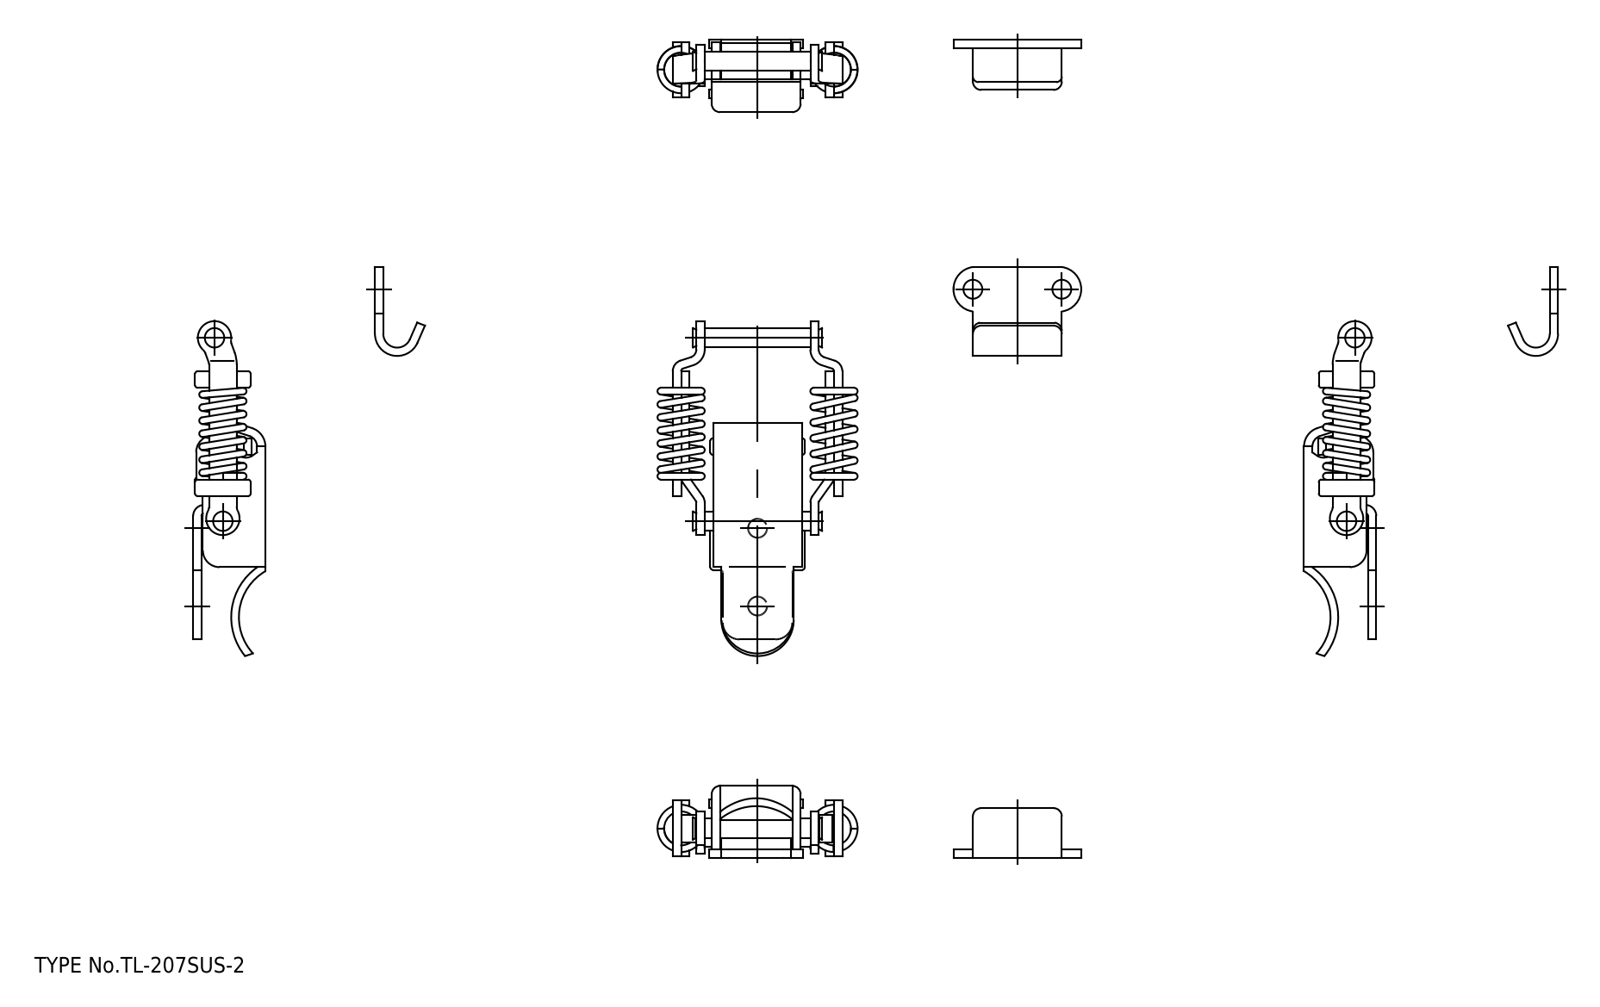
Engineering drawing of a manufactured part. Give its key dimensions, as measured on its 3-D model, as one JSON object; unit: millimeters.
{"part_name": "armA; base; spring; armB (+2 more)", "step_written_by": "spGate 19.8.4 (****-****-****-****) (AUTOMOTIVE_DESIGN)", "units": "millimeters", "bodies": {"solids": 7, "faces": 254, "planar": 124, "cylindrical": 98, "other": 32}, "overall_size": [69.99, 36, 13], "volume_mm3": 4850, "surface_area_mm2": 8333, "round_holes": [[3.2, 2], [3.4, 2]], "round_bosses_or_shafts": [[3.5, 2]], "partial_cylinders_radius": [[0.5, 16], [1.5, 10], [2, 9], [3, 8], [1.75, 2], [4.04, 2], [6.5, 2], [2.5, 1]], "face_to_face_distances": [1.5, 21.75, 5.75, 7.25, 20.25, 11.5, 13, 14.5, 27.5, 23.25], "hole_center_spacings": [43.73, 57.55, 14, 16]}
